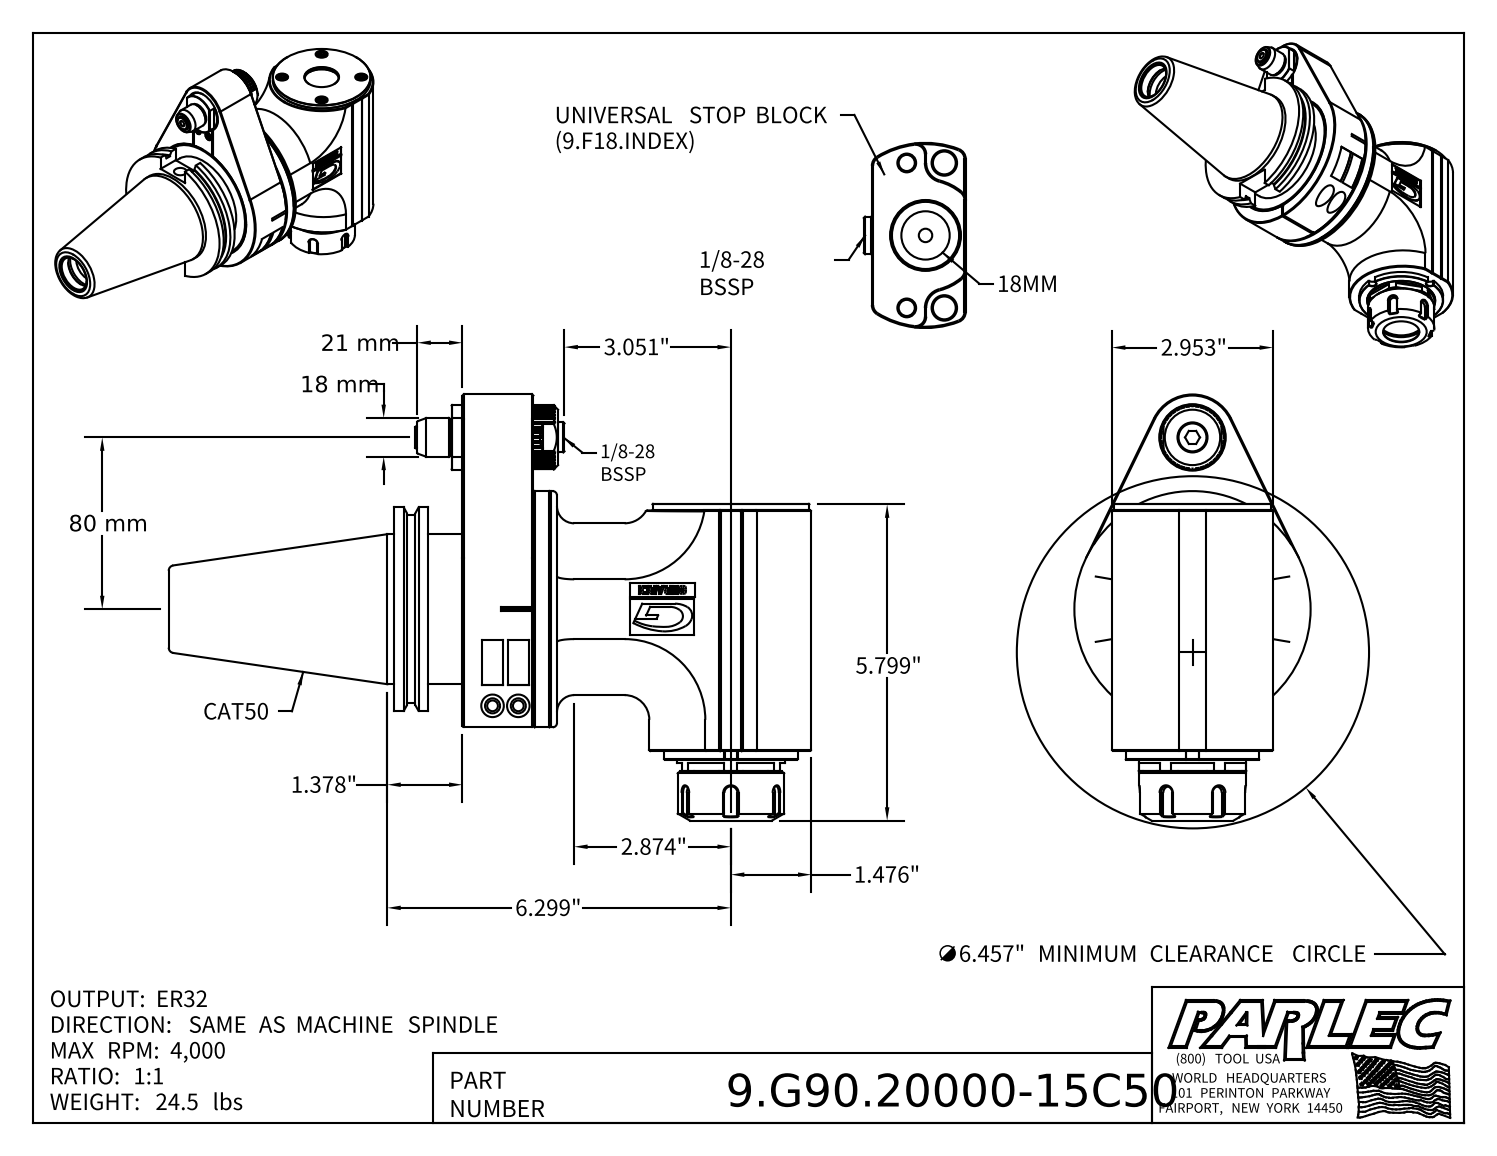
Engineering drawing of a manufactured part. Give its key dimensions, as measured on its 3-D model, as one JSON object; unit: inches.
{"part_name": "9.G90.20000-15C50; 9_G90_20000; 9_GA2_458_1 (Classic, Type 2, Cat50, 80mm)", "step_written_by": "Autodesk Inventor 2022 (AUTOMOTIVE_DESIGN)", "units": "inches", "bodies": {"solids": 4, "faces": 882, "planar": 491, "cylindrical": 166, "other": 225}, "overall_size": [11.783, 7.815, 4.331], "volume_in3": 102.7, "surface_area_in2": 298.9, "round_holes": [[0.197, 10], [0.335, 3], [0.157, 2], [0.236, 2], [0.276, 2], [0.413, 2], [0.13, 1], [0.165, 1], [0.433, 1], [0.551, 1], [0.598, 1], [0.709, 1]], "round_bosses_or_shafts": [[0.394, 2], [4.331, 1], [4.016, 1], [3.875, 1], [3.593, 1], [3.524, 1], [3.15, 1], [2.874, 1]], "partial_cylinders_radius": [[0.118, 7], [0.085, 2], [0.315, 2], [1.575, 2], [0.079, 1], [0.098, 1], [0.138, 1], [0.181, 1]], "face_to_face_distances": [1.299, 0.315, 0.626, 0.984, 0.118, 2.953, 0.197, 1.925, 0.941, 1.567], "hole_center_spacings": [1.87, 0.968, 2.645, 3.239, 3.613, 0.217, 0.538, 0.817]}
